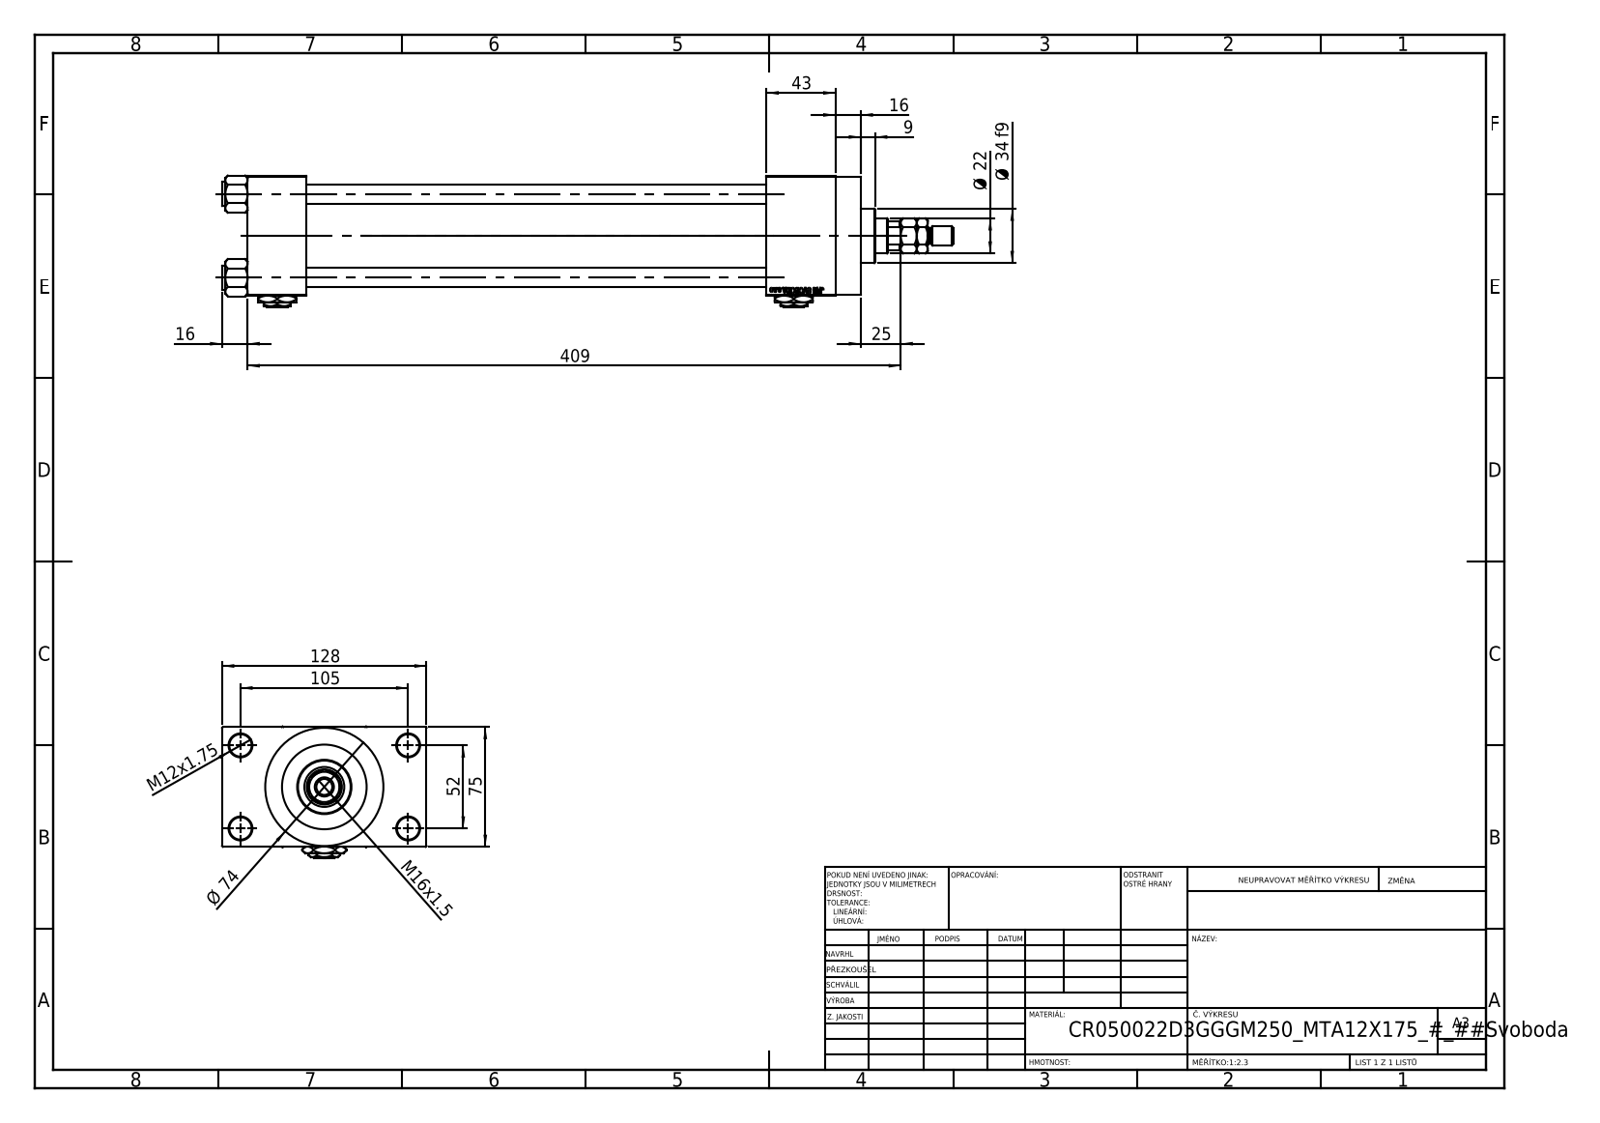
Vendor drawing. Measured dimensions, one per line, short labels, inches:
name: MTA; V215CR_D_TYCINKA; NUT_M5_D; V215CR_D_Body (+3 more)
written by: SolidWorks 2019 (CONFIG_CONTROL_DESIGN)
unit: in
bodies: 14 solids, 1254 faces (560 planar, 104 cylindrical, 590 other)
size: 18.031 × 5.039 × 3.239
volume: 68.1 in³; area: 462.9 in²
holes: 4× ⌀0.472, 4× ⌀0.551, 2× ⌀0.276, 2× ⌀0.825, 2× ⌀1.181, 1× ⌀0.413, 1× ⌀0.866, 1× ⌀0.984, 1× ⌀1.614, 1× ⌀1.969, 1× ⌀2.087
bosses: 4× ⌀0.591, 1× ⌀2.913, 1× ⌀2.205, 1× ⌀1.339, 1× ⌀0.472, 1× ⌀0.394
rounds: 1× R0.413
face distances: 2.953, 11.339, 1.457, 12.795, 1.043, 3.996, 14.488, 13.031, 1.693, 0.63
hole spacings: 1.037, 1.456, 2.059, 2.3, 2.307, 3.096, 3.715, 2.047
